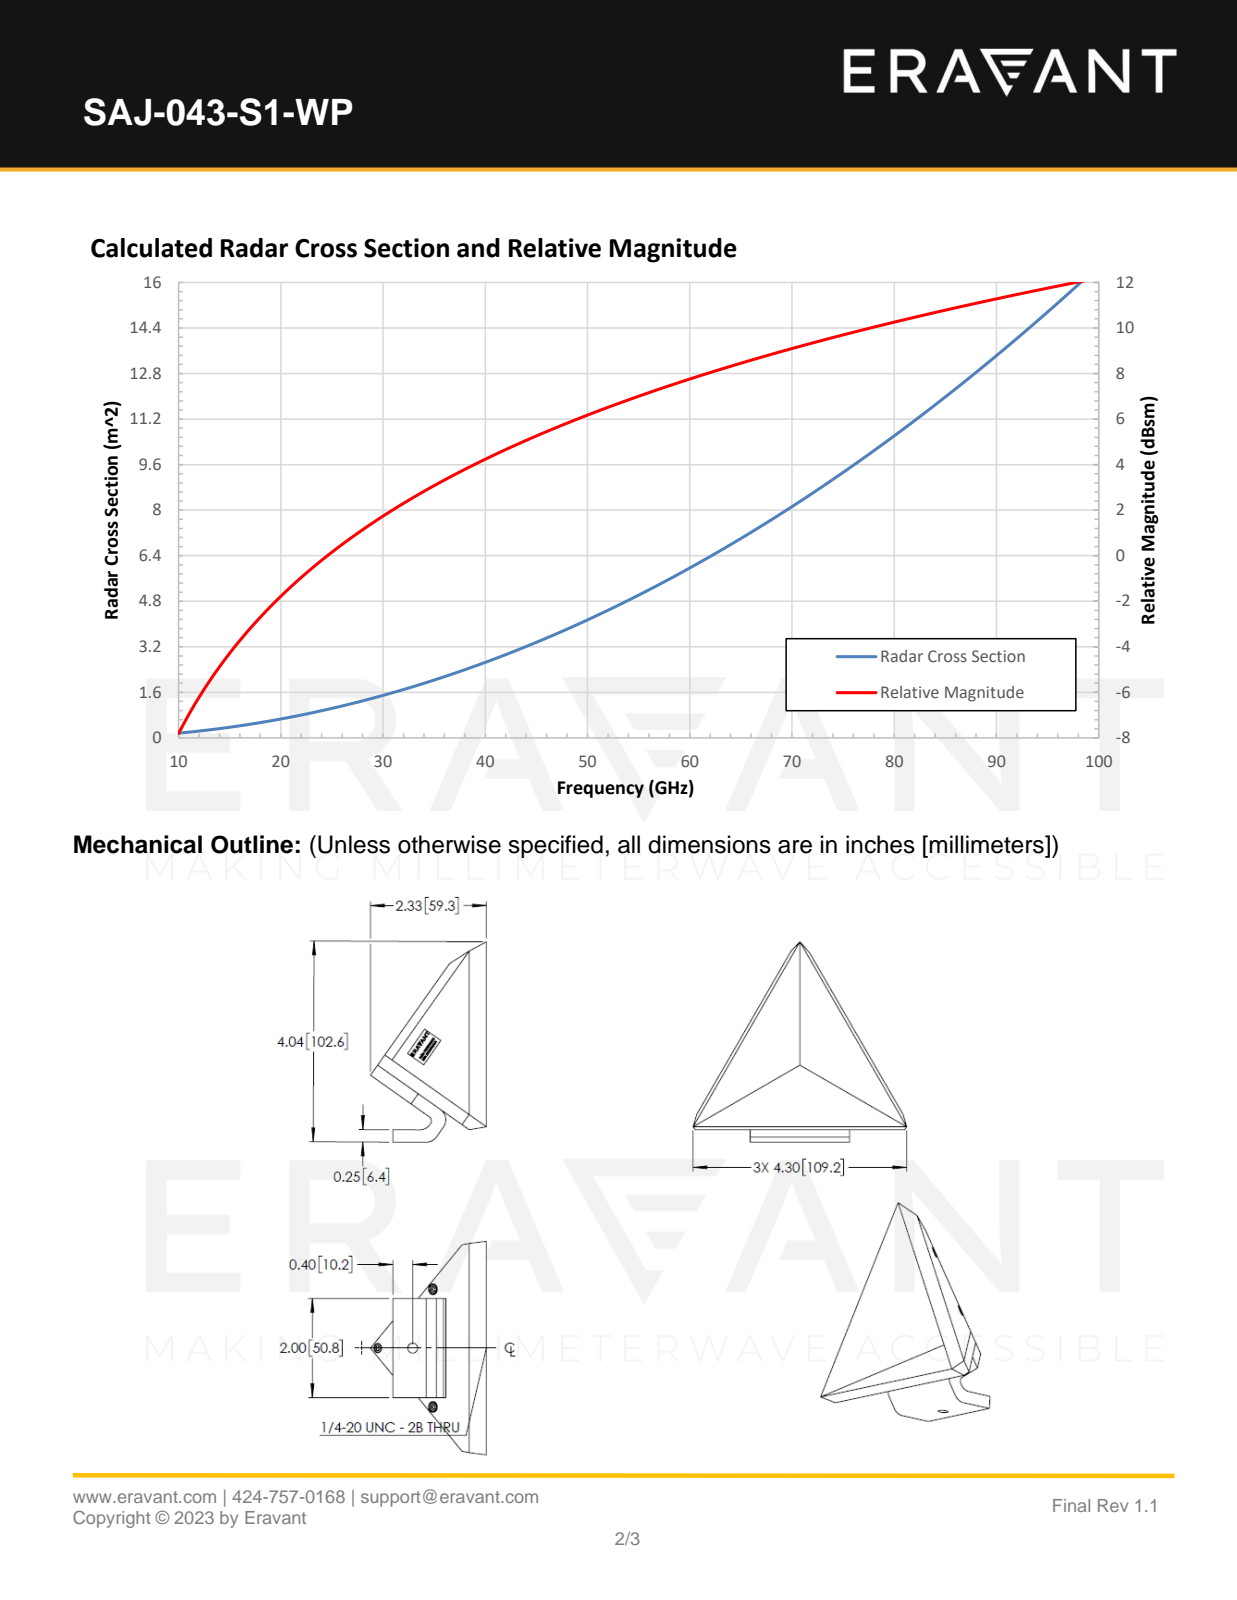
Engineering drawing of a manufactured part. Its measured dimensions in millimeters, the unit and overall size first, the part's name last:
Units: millimetres
Overall size (bounding box): 111.4 × 109.2 × 63.6
Round holes (diameter × count): ⌀5.1 ×1
Partial cylindrical surfaces — rounded edges, fillets, slot ends (radius × count): R6.4 ×3, R2.5 ×1
Main face-to-face distances: 6.4, 12.7, 6.4, 50.8
Volume: 78 000 mm³ · Surface area: 31 720 mm²
Bodies: 4 solids, 35 faces (29 planar, 6 cylindrical, 0 other)
Part name (STEP PRODUCT): SAJ-043-S1
STEP written by: SolidWorks 2016 (CONFIG_CONTROL_DESIGN)
